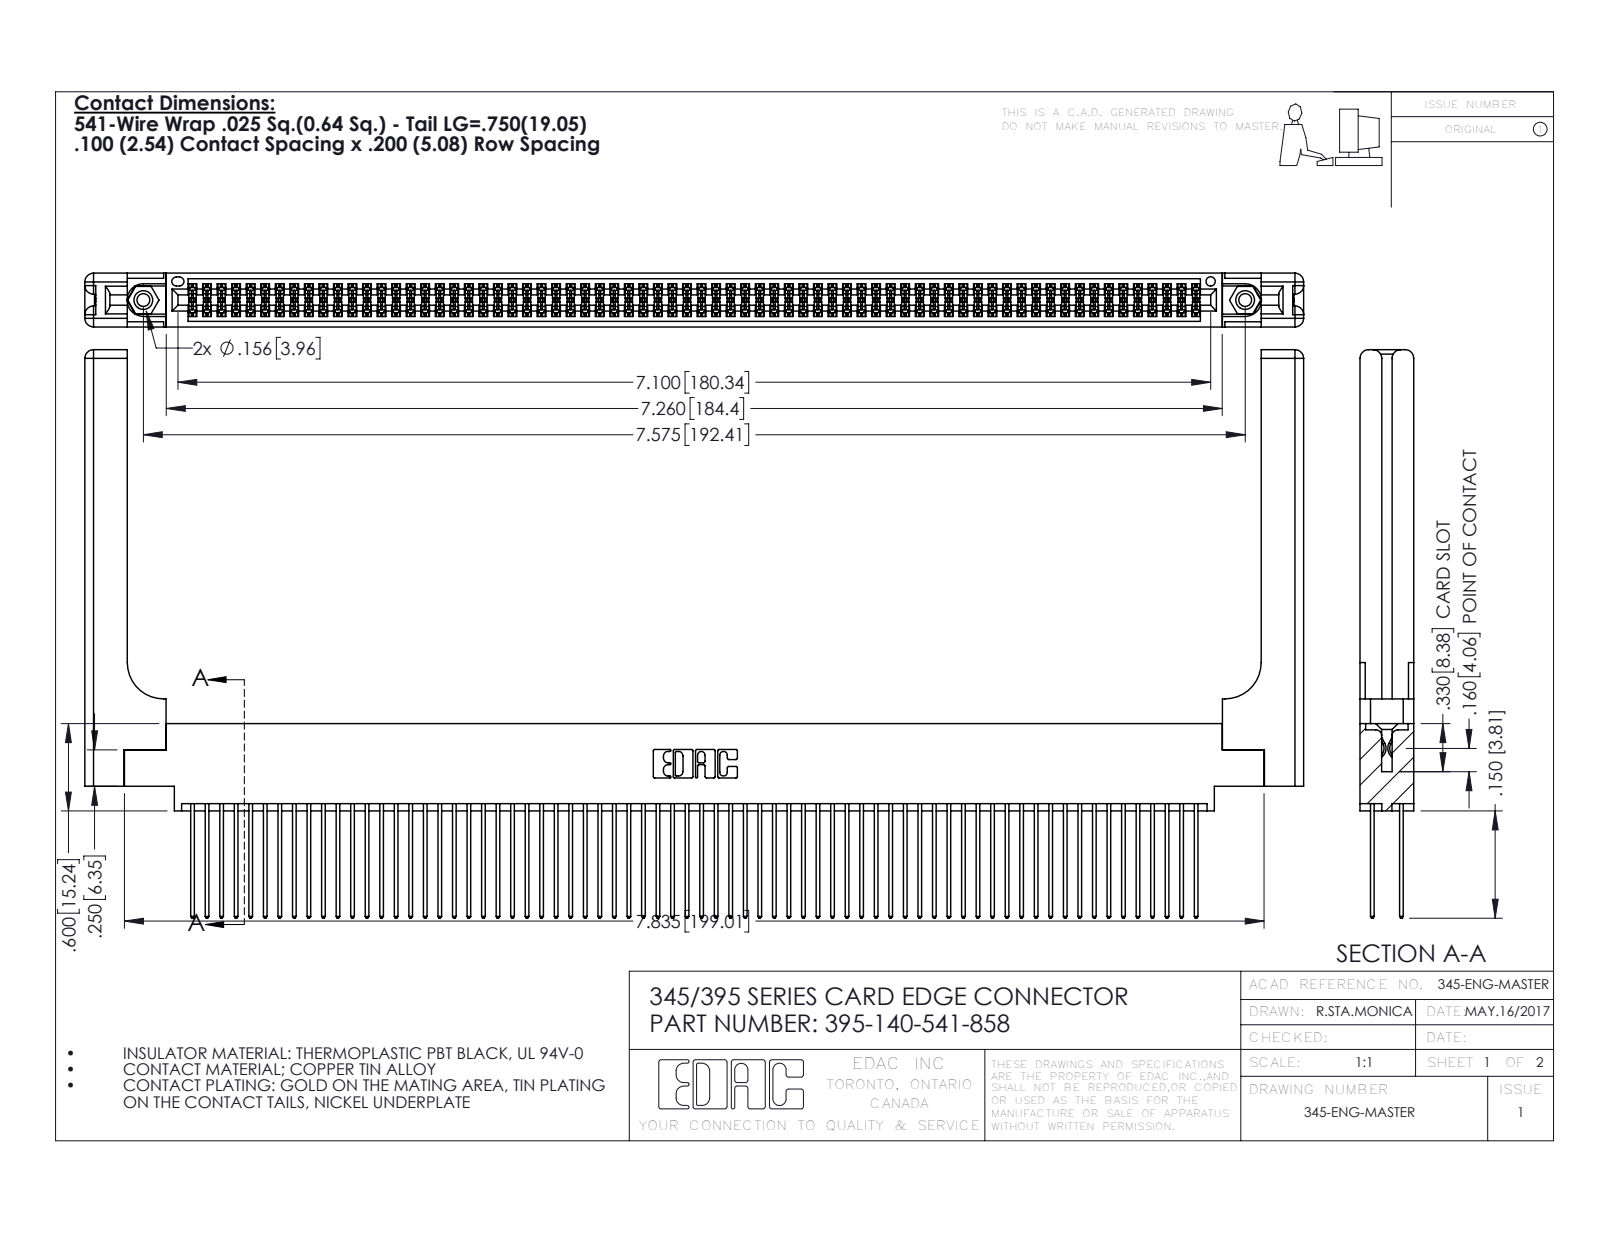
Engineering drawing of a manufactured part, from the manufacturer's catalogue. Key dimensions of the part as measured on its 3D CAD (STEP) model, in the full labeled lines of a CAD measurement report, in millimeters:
Part name (STEP PRODUCT): 345-250-001_345-250-001-102; 345 Part_0.170 Offset - 0.156 Dia-TH; 345-292-001_345-293-141; 345-220-058_345-220-058 (+1 more)
STEP written by: SolidWorks 2016 (CONFIG_CONTROL_DESIGN)
Units: millimetres
Bodies: 145 solids, 7386 faces (4852 planar, 2474 cylindrical, 60 other)
Overall size (bounding box): 212.8 × 99.2 × 9.4
Volume: 30 100 mm³ · Surface area: 41 480 mm²
Round holes (diameter × count): ⌀2.3 ×2, ⌀3.2 ×2, ⌀4 ×2, ⌀1.6 ×1
Round bosses / shafts (diameter × count): ⌀3.9 ×2
Partial cylindrical surfaces — rounded edges, fillets, slot ends (radius × count): R0.2 ×210, R0.3 ×140, R0.3 ×22, R1.5 ×16, R0.2 ×6, R0.8 ×6, R0.7 ×3, R0.4 ×2
Main face-to-face distances: 1.8, 7.6, 2.5, 6.9, 0.6, 5.1, 9.4, 5.7, 4.4, 3.8
Hole centre spacings: 6.9, 186.4, 192.4
